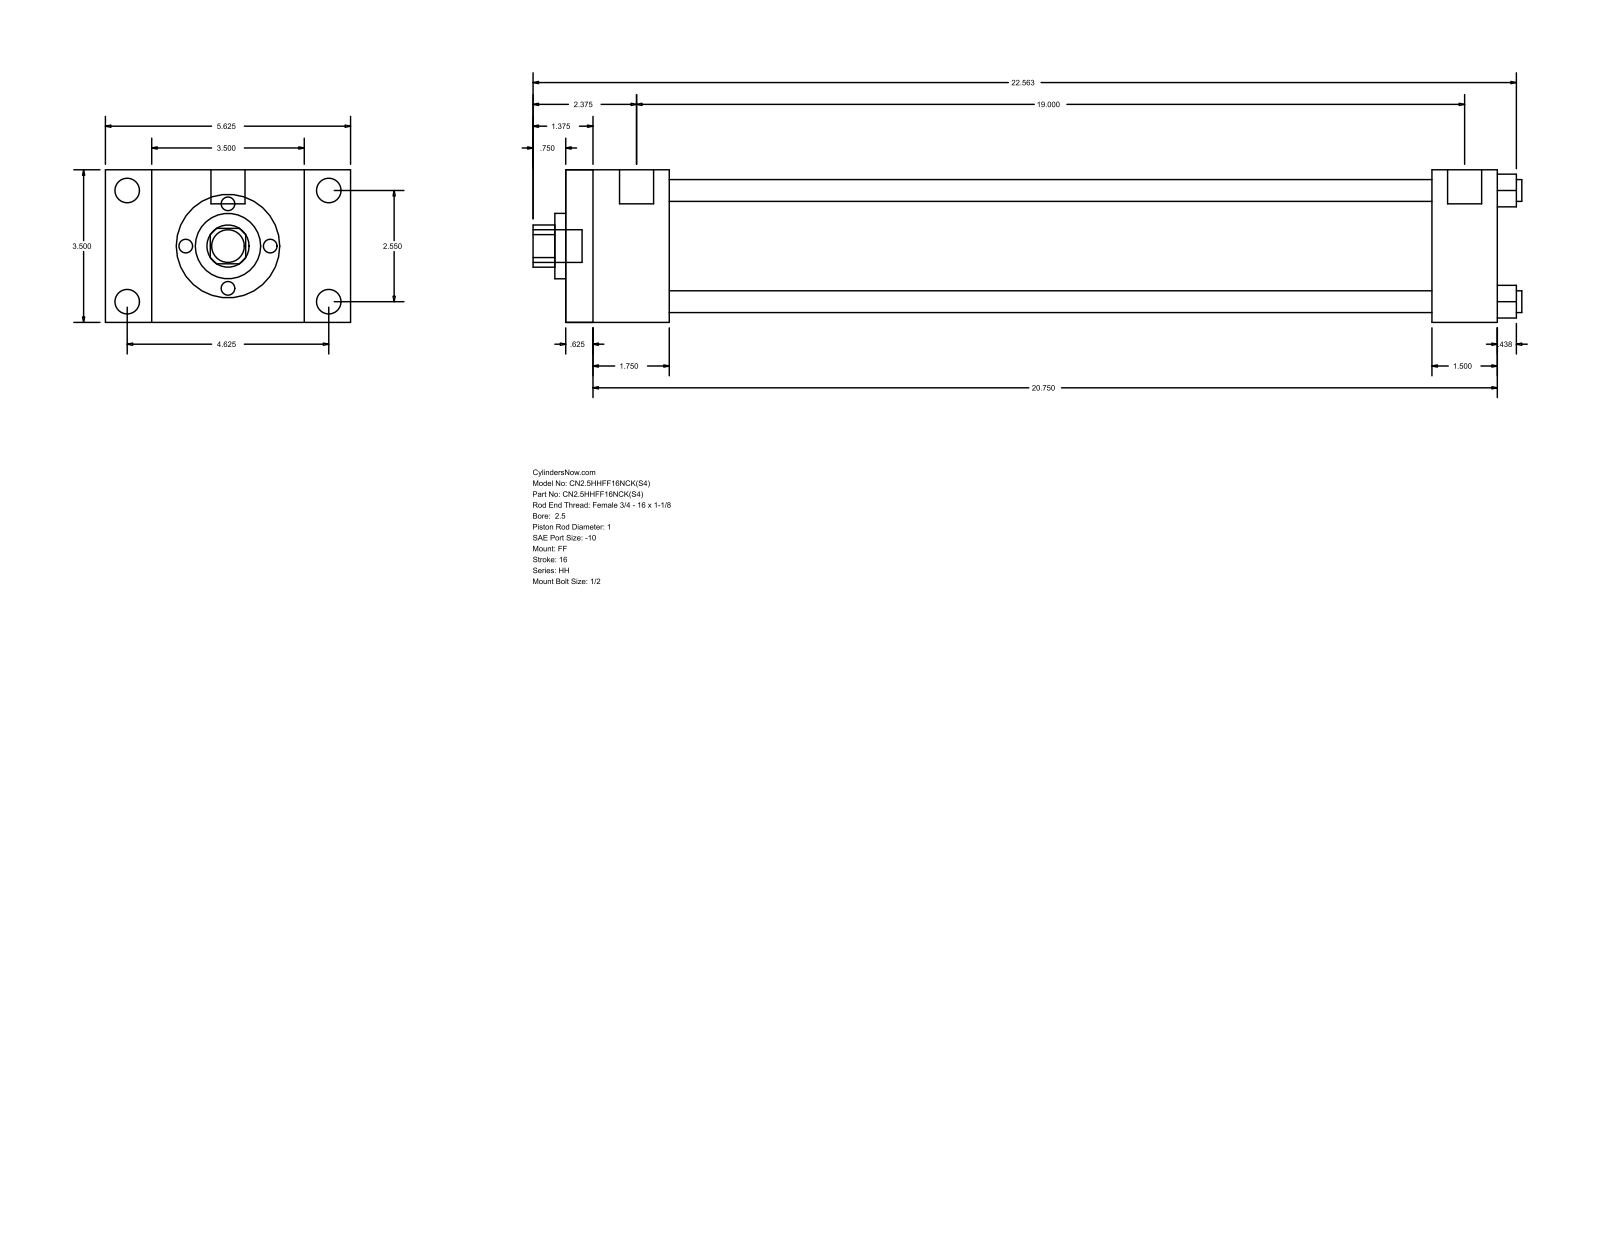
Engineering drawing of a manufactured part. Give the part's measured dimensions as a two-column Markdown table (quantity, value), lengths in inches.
| quantity | value |
| --- | --- |
| part name | HH_FF__0250_1 |
| STEP written by | GSSL Pune (CONFIG_CONTROL_DESIGN) |
| units | inches |
| bodies | 0 solids, 92 faces (64 planar, 28 cylindrical, 0 other) |
| overall size | 22.687 × 5.625 × 3.5 |
| round holes (diameter × count) | 0.5 × 4, 1 × 1, 1.5 × 1, 2.875 × 1 |
| round bosses / shafts (diameter × count) | 0.563 × 4, 0.219 × 4, 0.781 × 2, 0.75 × 1 |
| partial cylindrical surfaces (radius × count) | 0.484 × 1 |
| main face-to-face distances | 3.5, 21.375, 0.625, 20.75, 2.375, 1.75, 19, 19.875, 19.25, 17.5 |
| hole center spacings | 1.803, 2.55, 3.606 |
